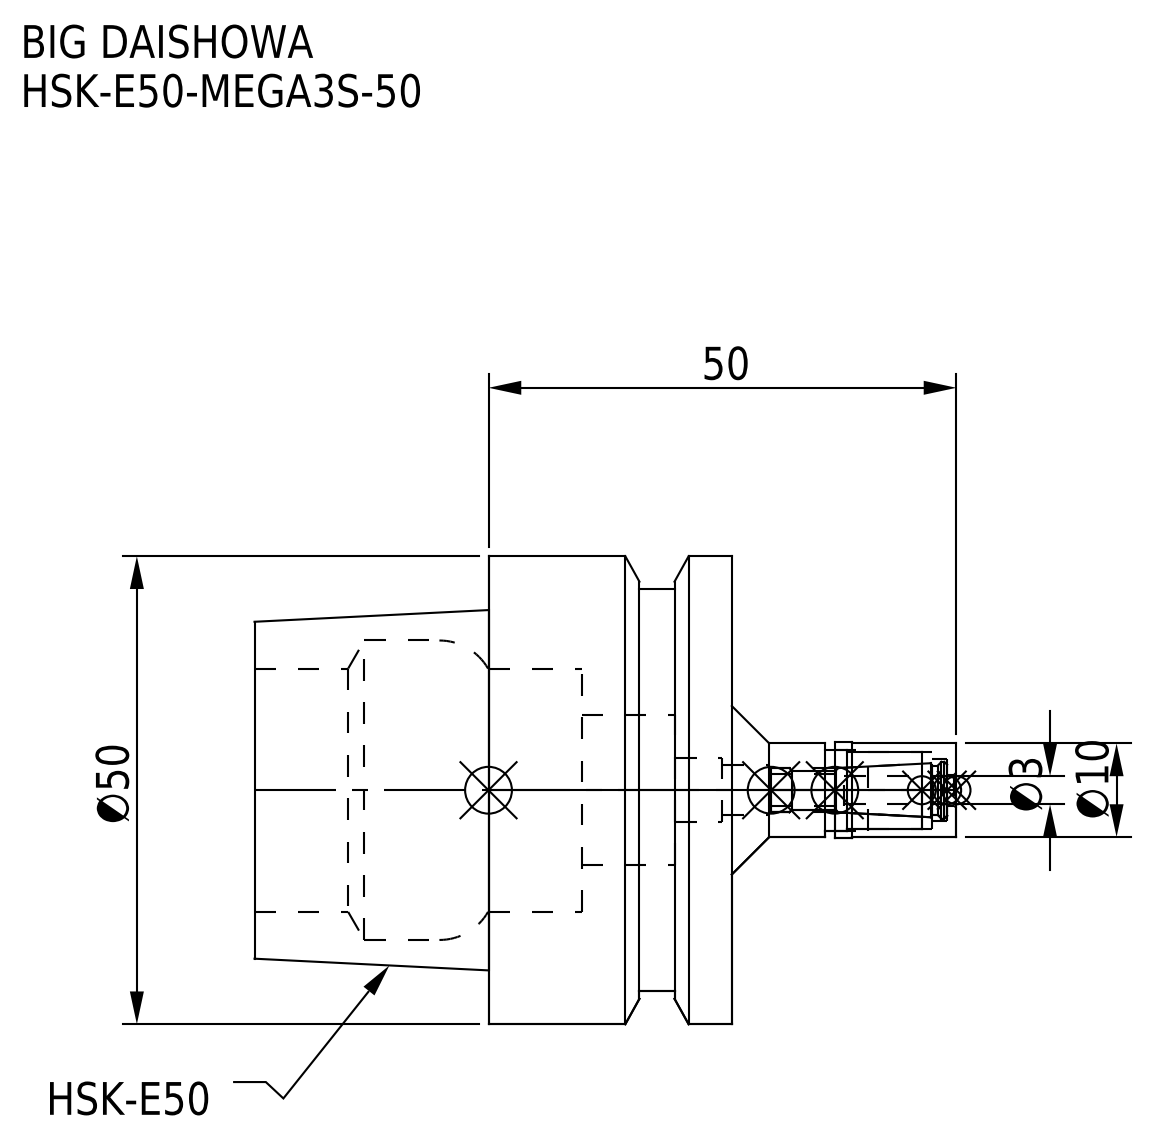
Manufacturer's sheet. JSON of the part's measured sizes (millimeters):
{"part_name": "MGN3S_1.stp; HSK-E50-MEGA3S-50-030.stp; HE50MS03040-030_ASM.stp; HSK-E50-MEGA3S-50-030-FreeParts (+3 more)", "step_written_by": "SolidWorks 2019 (CONFIG_CONTROL_DESIGN)", "units": "millimeters", "bodies": {"solids": 2, "faces": 74, "planar": 18, "cylindrical": 40, "other": 16}, "overall_size": [75, 50, 50], "volume_mm3": 53239, "surface_area_mm2": 17035, "round_holes": [[3.3, 1], [4.7, 1], [5.3, 1], [6.6, 1], [6.8, 1], [8.2, 1], [8.7, 1], [16, 1], [26, 1], [32, 1]], "round_bosses_or_shafts": [[50, 1], [43, 1], [10.3, 1], [10, 1]], "face_to_face_distances": [26, 25, 51, 16.05, 9.95, 34.95, 10, 6.05, 19.95, 44.95]}
